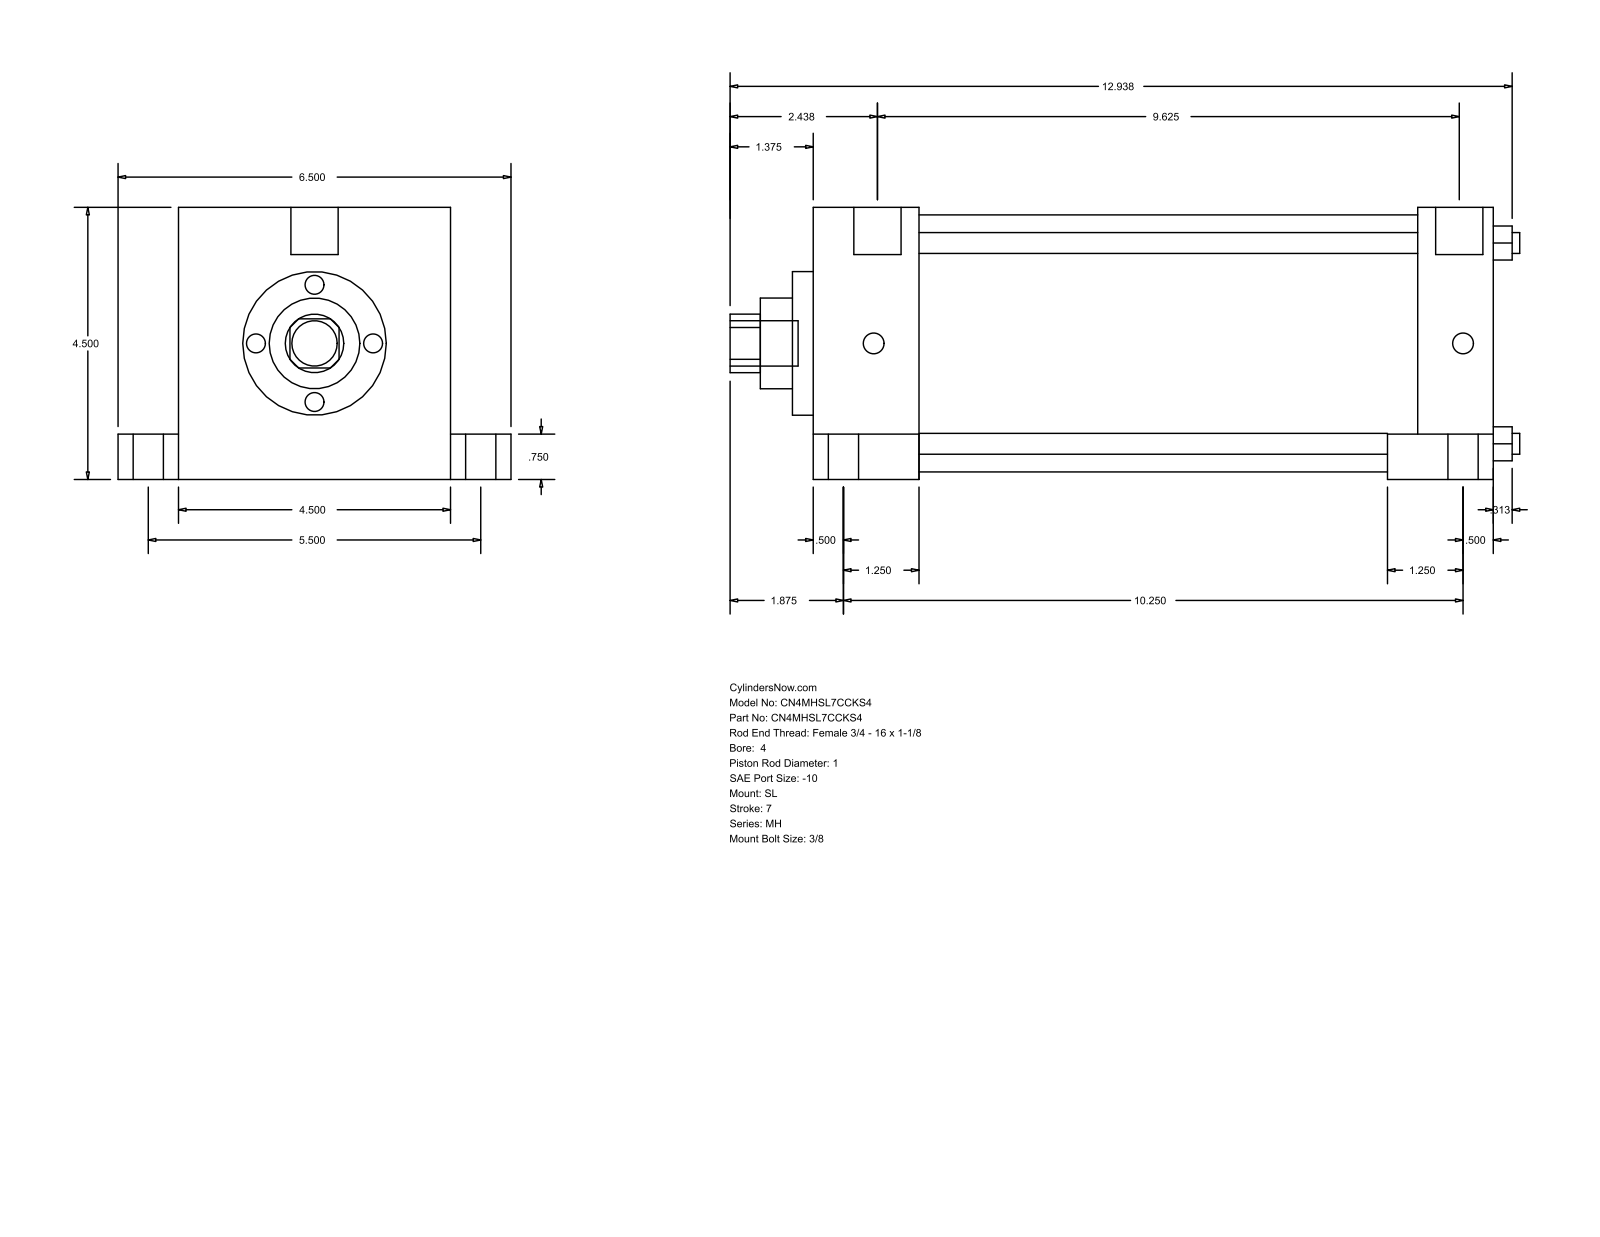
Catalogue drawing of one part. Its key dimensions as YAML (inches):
part_name: "MH_SL__0400_1"
step_written_by: "GSSL Pune (CONFIG_CONTROL_DESIGN)"
units: inches
bodies: {solids: 0, faces: 110, planar: 77, cylindrical: 33, other: 0}
overall_size: [13.063, 6.5, 4.5]
round_holes:
  - {diameter: 0.345, count: 4}
  - {diameter: 1, count: 1}
  - {diameter: 1.5, count: 1}
  - {diameter: 2.375, count: 1}
  - {diameter: 4.25, count: 1}
round_bosses_or_shafts:
  - {diameter: 0.75, count: 5}
  - {diameter: 0.5, count: 4}
  - {diameter: 0.344, count: 4}
  - {diameter: 0.781, count: 2}
partial_cylinders:
  - {radius: 0.484, count: 1}
face_to_face_distances: [4.5, 11.25, 1.75, 9.5, 10, 8.25, 1.25, 1, 5.5, 0.75]
hole_center_spacings: [2.347, 3.32, 4.695]
